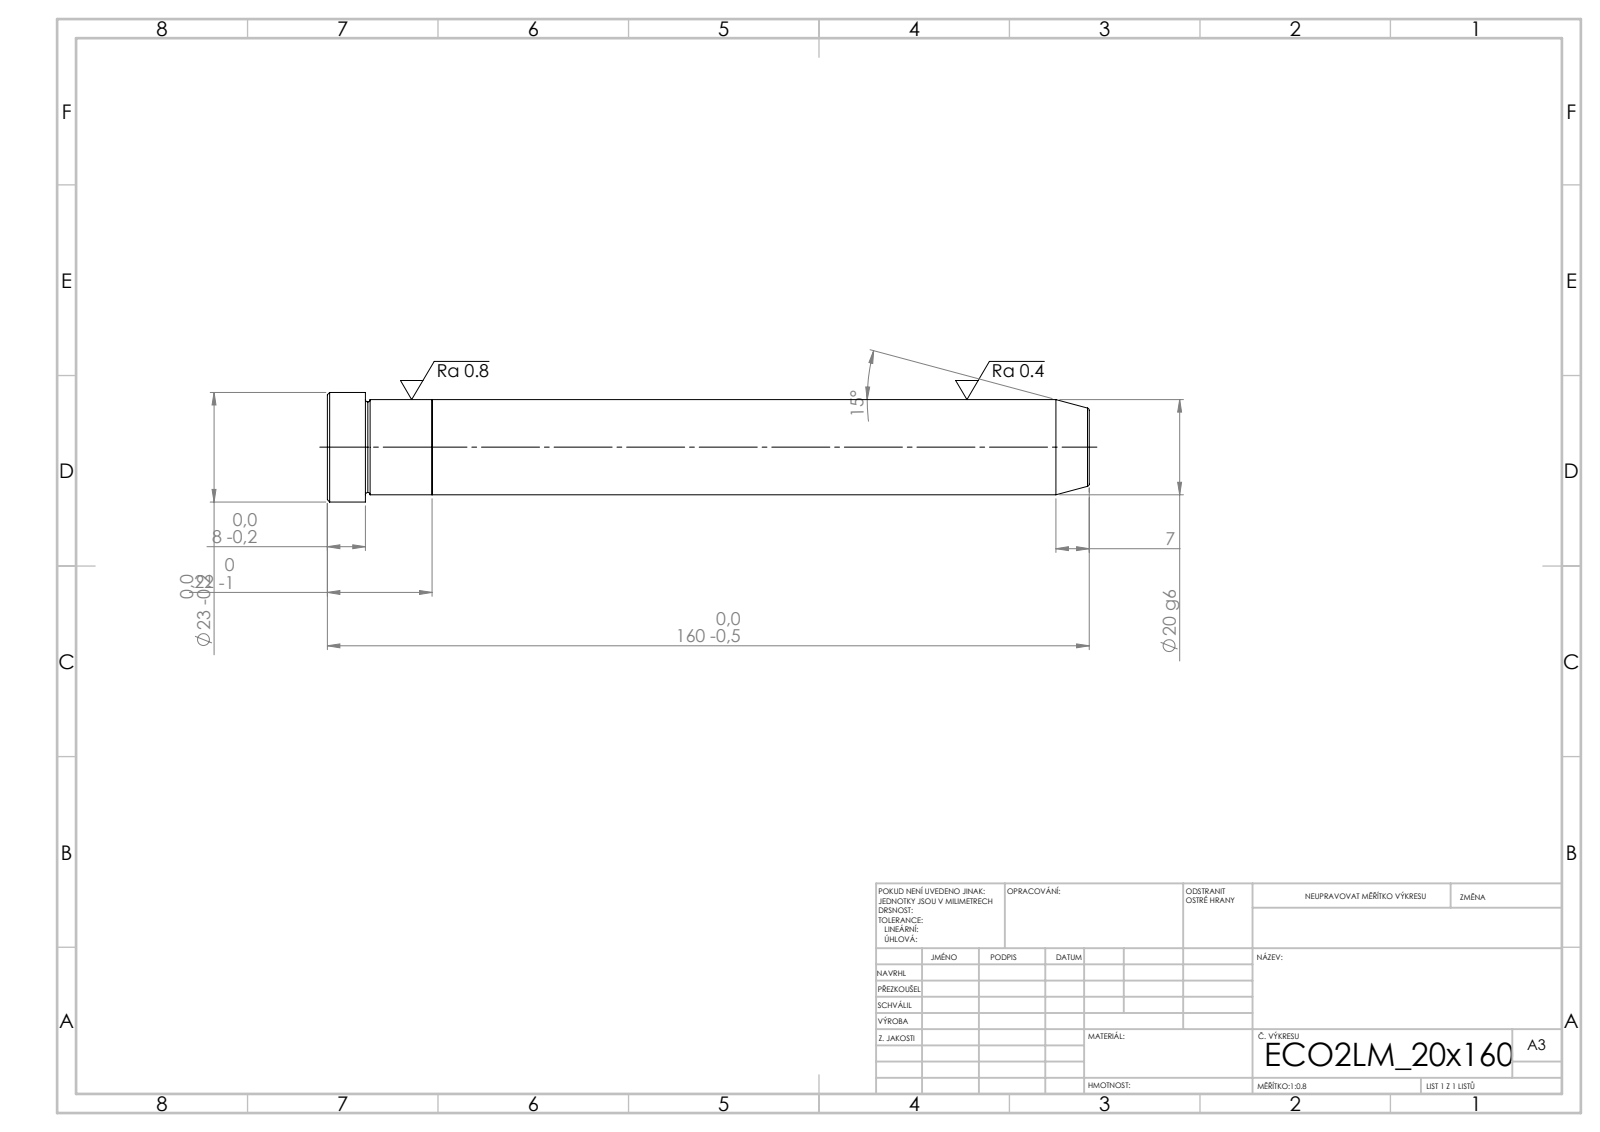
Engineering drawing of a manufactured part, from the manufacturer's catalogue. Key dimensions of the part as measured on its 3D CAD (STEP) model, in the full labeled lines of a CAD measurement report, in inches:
STEP written by: SolidWorks 2019 (CONFIG_CONTROL_DESIGN)
Units: inches
Bodies: 2 solids, 21 faces (5 planar, 6 cylindrical, 10 other)
Overall size (bounding box): 6.299 × 0.906 × 0.906
Volume: 3.091 in³ · Surface area: 17.76 in²
Round bosses / shafts (diameter × count): ⌀0.906 ×1, ⌀0.787 ×1
Main face-to-face distances: 0.866, 5.433, 6.299, 5.984, 0.551, 0.315
